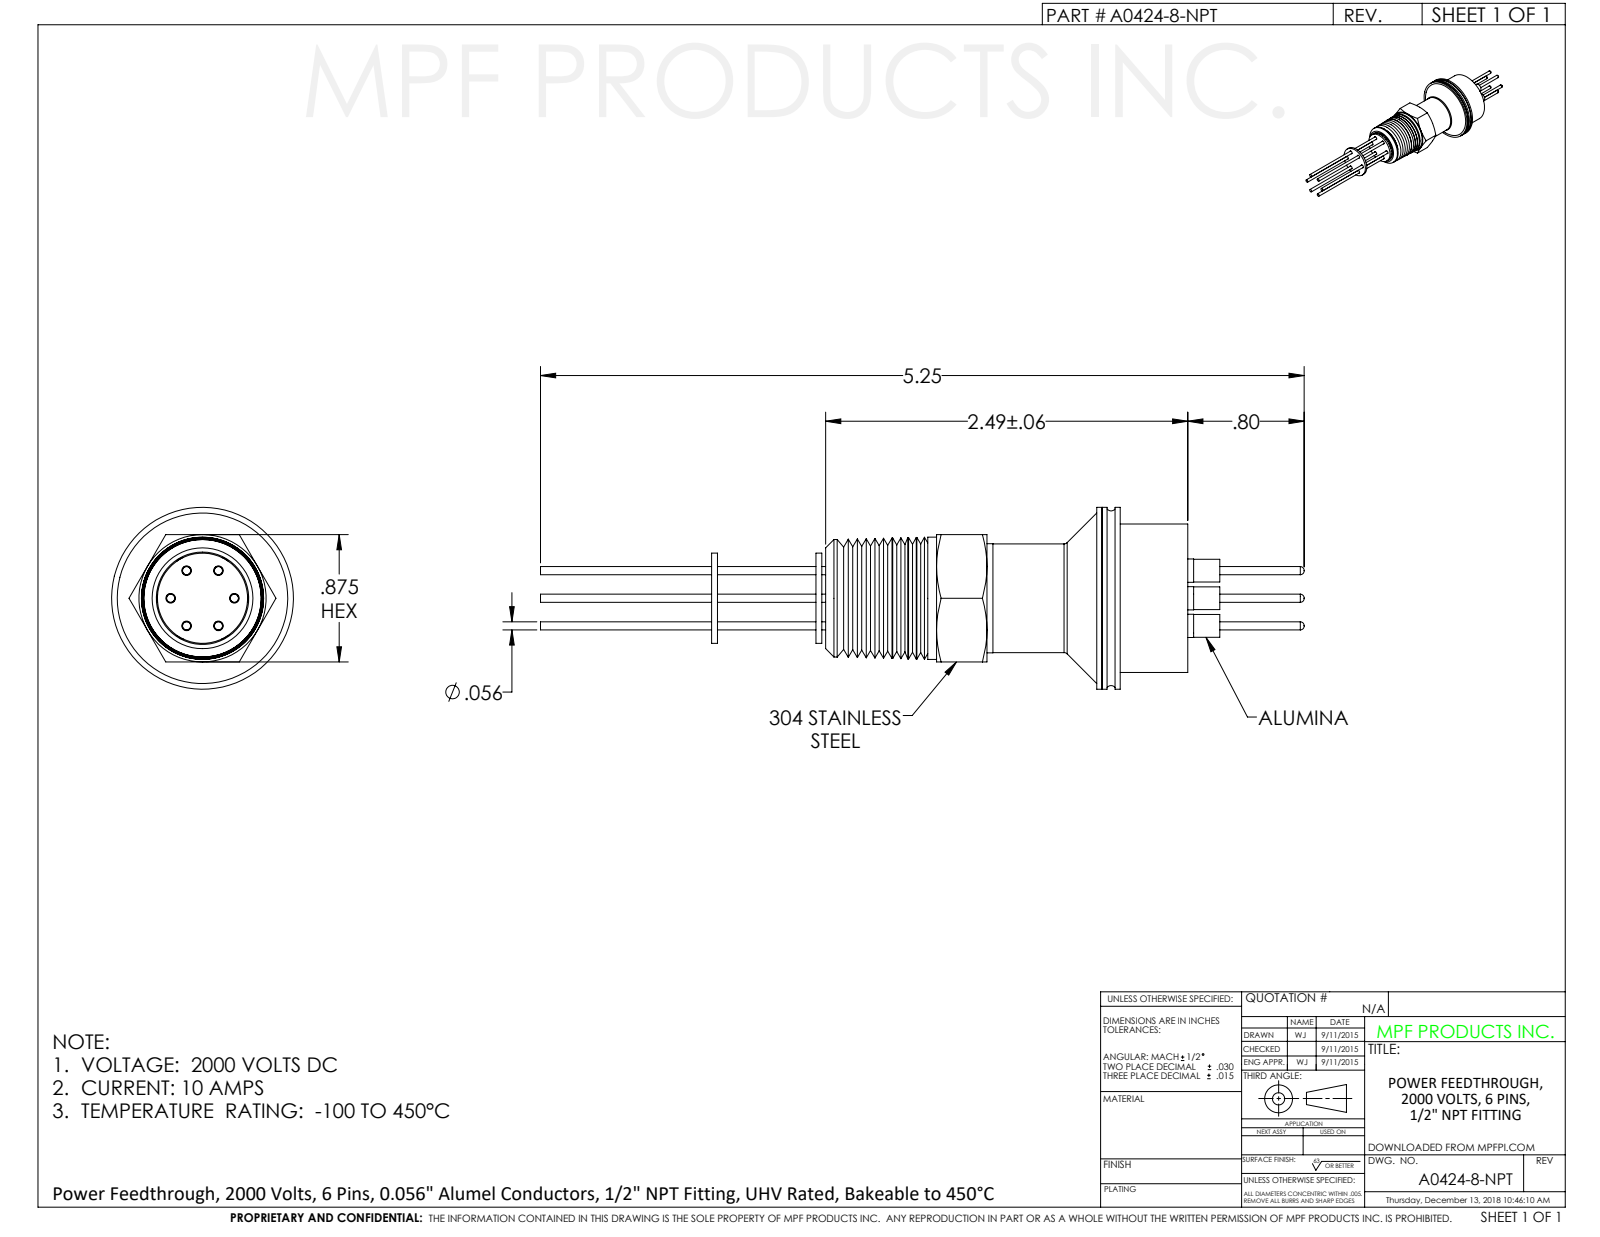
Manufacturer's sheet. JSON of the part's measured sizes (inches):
{"part_name": "A0424-8-NPT", "step_written_by": "SolidWorks 2012 (CONFIG_CONTROL_DESIGN)", "units": "inches", "bodies": {"solids": 1, "faces": 293, "planar": 57, "cylindrical": 130, "other": 106}, "overall_size": [5.25, 1.25, 1.25], "volume_in3": 0.647, "surface_area_in2": 25.96, "round_holes": [[0.625, 1], [0.675, 1], [0.94, 1], [0.96, 1], [0.97, 1]], "round_bosses_or_shafts": [[0.187, 6], [0.171, 6], [0.056, 6], [1.25, 1], [1.02, 1], [0.957, 1], [0.84, 1], [0.75, 1]], "face_to_face_distances": [0.05, 0.43, 0.38, 0.04, 2.629, 0.875, 2.719, 3.196, 3.236, 2.669], "hole_center_spacings": [0.269, 0.19, 0.38, 0.187, 0.193, 0.269]}
